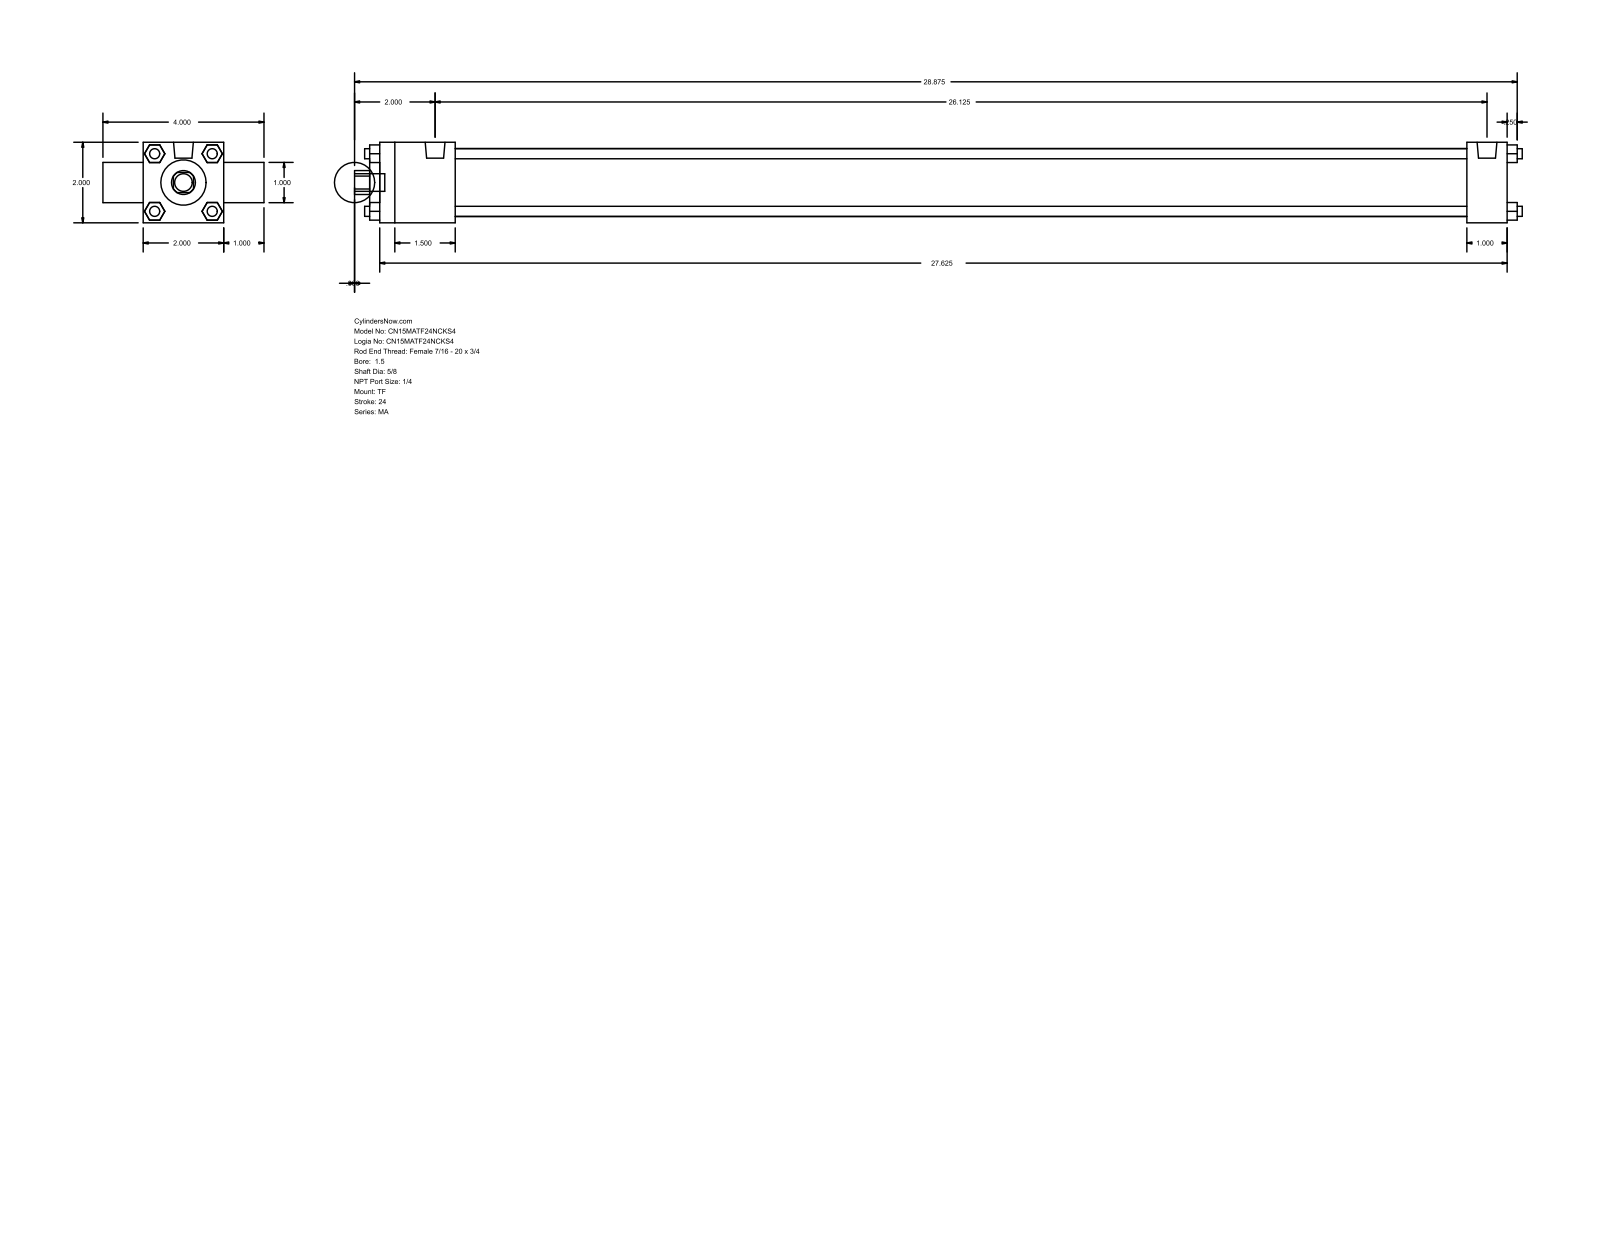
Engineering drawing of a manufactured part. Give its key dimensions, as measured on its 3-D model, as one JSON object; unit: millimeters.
{"part_name": "MA_TF__0150_0.625", "step_written_by": "GSSL Pune (CONFIG_CONTROL_DESIGN)", "units": "millimeters", "bodies": {"solids": 0, "faces": 120, "planar": 92, "cylindrical": 28, "other": 0}, "overall_size": [736.6, 101.6, 50.8], "round_holes": [[15.88, 1], [25.4, 1], [28.57, 1], [42.93, 1]], "round_bosses_or_shafts": [[6.35, 4], [7.94, 3], [12.49, 2], [11.11, 1]], "partial_cylinders_radius": [[7.54, 1]], "face_to_face_distances": [50.8, 711.2, 25.4, 76.2, 47.62, 685.79, 638.17, 663.58, 25.41, 717.55]}
